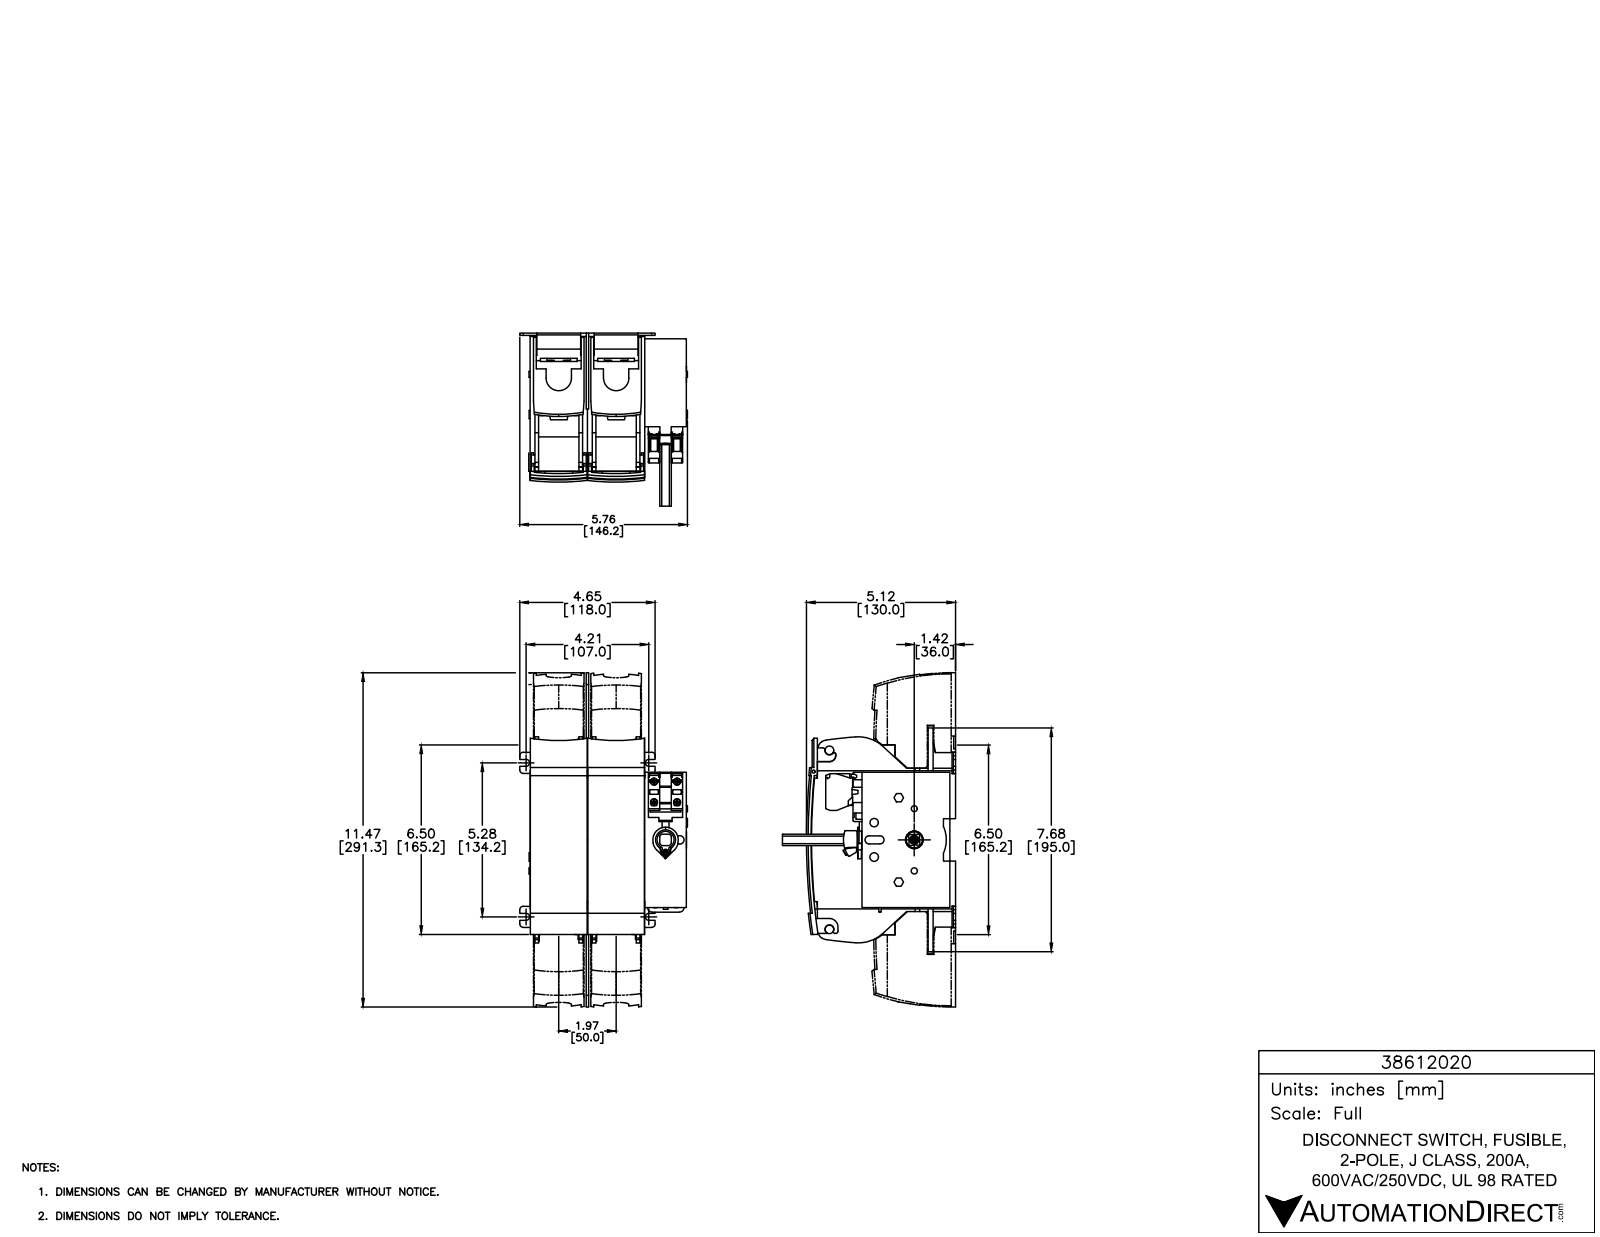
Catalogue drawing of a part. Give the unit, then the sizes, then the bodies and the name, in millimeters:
Units: millimetres
Overall size (bounding box): 291.3 × 146.2 × 130
Round holes (diameter × count): ⌀7 ×4, ⌀11 ×4, ⌀5.3 ×2, ⌀5.4 ×2, ⌀7.5 ×2, ⌀8 ×2, ⌀2.5 ×1, ⌀2.6 ×1, ⌀3.3 ×1, ⌀7.2 ×1, ⌀15.3 ×1, ⌀15.8 ×1
Round bosses / shafts (diameter × count): ⌀7.5 ×2, ⌀7.3 ×2, ⌀5.2 ×2, ⌀5.2 ×2, ⌀16 ×1, ⌀8 ×1, ⌀5 ×1
Partial cylindrical surfaces — rounded edges, fillets, slot ends (radius × count): R1.5 ×16, R3 ×12, R1 ×5, R1.8 ×4, R2 ×4, R3.5 ×4, R5.4 ×4, R7.5 ×4
Main face-to-face distances: 50, 48.9, 51.1, 1, 4.2, 45.8, 100, 2.1, 3.2, 7.4
Hole centre spacings: 16.6, 27.1, 30.6, 37, 38.1, 39.1, 50, 54.8
Volume: 2 117 000 mm³ · Surface area: 279 900 mm²
Bodies: 11 solids, 1275 faces (874 planar, 309 cylindrical, 92 other)
Part name (STEP PRODUCT): 38612020
STEP written by: SolidWorks 2015 (AUTOMOTIVE_DESIGN)
